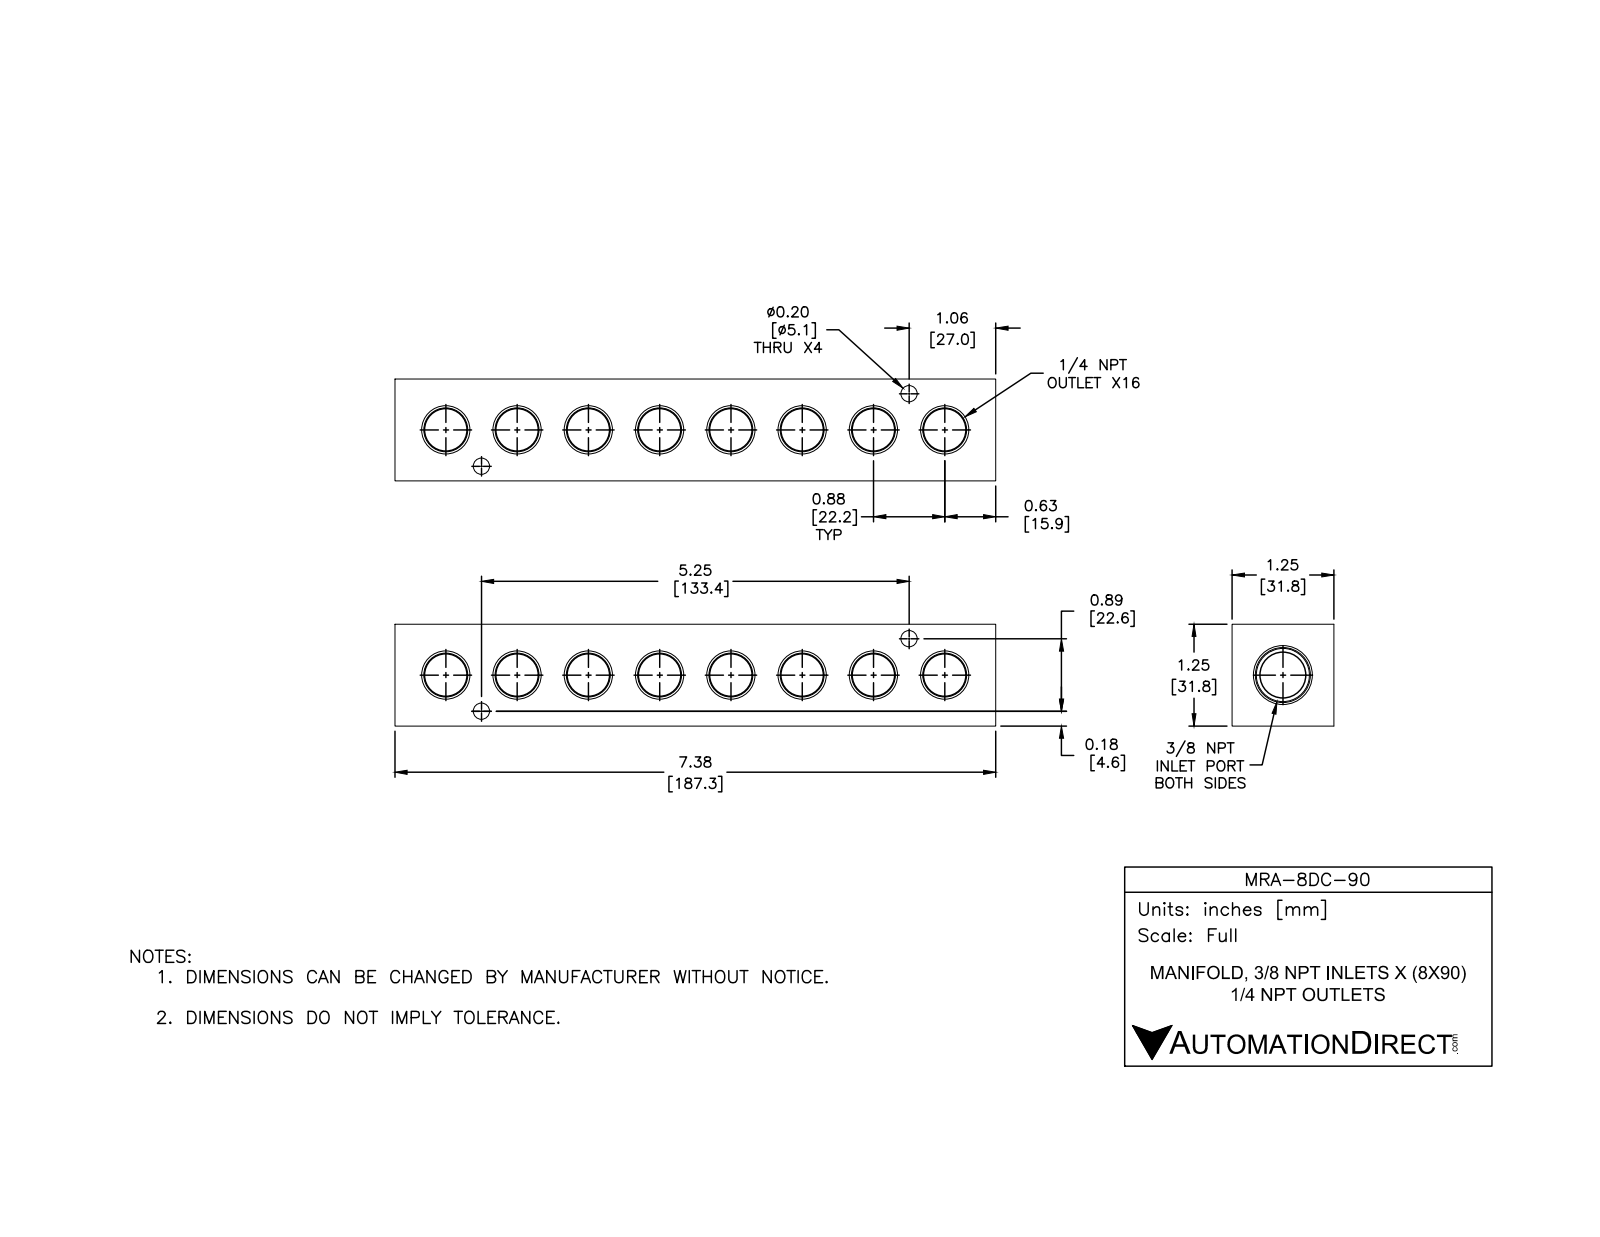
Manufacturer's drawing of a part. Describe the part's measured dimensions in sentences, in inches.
The part is named "MRA-8DC-90". Its 3-D file was written by "SolidWorks 2015 (CONFIG_CONTROL_DESIGN)". It is 1 solid with 166 faces: 42 planar, 52 cylindrical and 72 other. Overall it measures 7.375 by 1.25 by 1.25 inches. Its volume is 8.153 cubic inches and its surface area 58.82 square inches. Round holes: 4 of diameter 0.2, 1 of diameter 0.562. Partial cylindrical surfaces (rounded edges, fillets, slot ends): 16 of radius 0.219. The main face-to-face distances are 1.25, 7.375, 0.86, 0.39, 0.41, 6.965, 6.555. The hole center spacings are 5.324.
